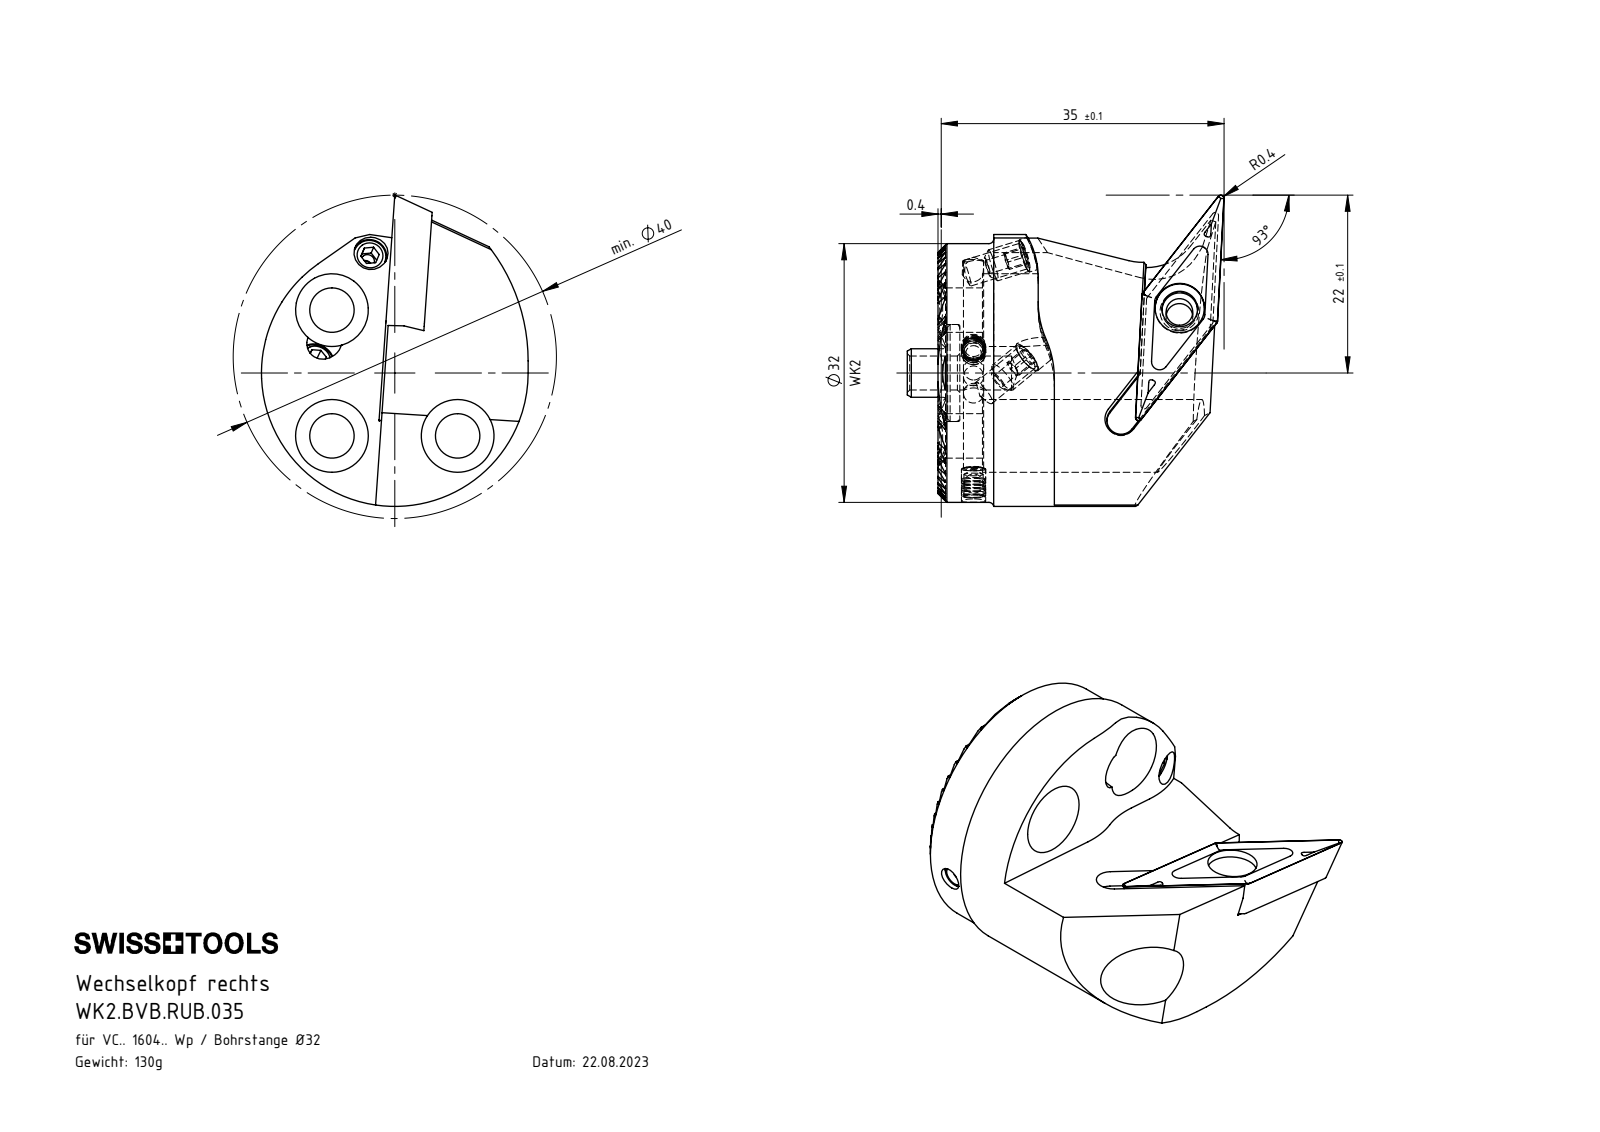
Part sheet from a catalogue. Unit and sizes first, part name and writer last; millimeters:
Units: millimetres
Overall size (bounding box): 39.2 × 38.5 × 33
Round holes (diameter × count): ⌀3.3 ×3, ⌀4.2 ×3, ⌀5.5 ×3, ⌀9 ×3, ⌀1.7 ×2, ⌀2.38 ×2, ⌀2.5 ×2, ⌀3 ×2, ⌀4.4 ×1, ⌀6.1 ×1, ⌀12 ×1
Round bosses / shafts (diameter × count): ⌀4 ×2, ⌀3 ×2, ⌀32 ×1, ⌀6 ×1
Partial cylindrical surfaces — rounded edges, fillets, slot ends (radius × count): R0.12 ×22, R12 ×3, R1.75 ×1, R7 ×1, R16.5 ×1, R23 ×1
Main face-to-face distances: 1.3, 2.6, 3.9, 5.2, 6.5, 12.99, 11.69, 14.29, 7.8, 10.39
Hole centre spacings: 11, 15.56, 22.01
Volume: 16 068 mm³ · Surface area: 8 536 mm²
Bodies: 9 solids, 362 faces (195 planar, 85 cylindrical, 82 other)
Part name (STEP PRODUCT): WK2-BVB.RUB.035_A_Fertigbearbeitung; WK2-ER1.001.012_A_Fertigbearbeitung; VCMT160404; WKX-ER1.004.005_A_PreviewCfg (+2 more)
STEP written by: SolidWorks 2017 (AUTOMOTIVE_DESIGN)
